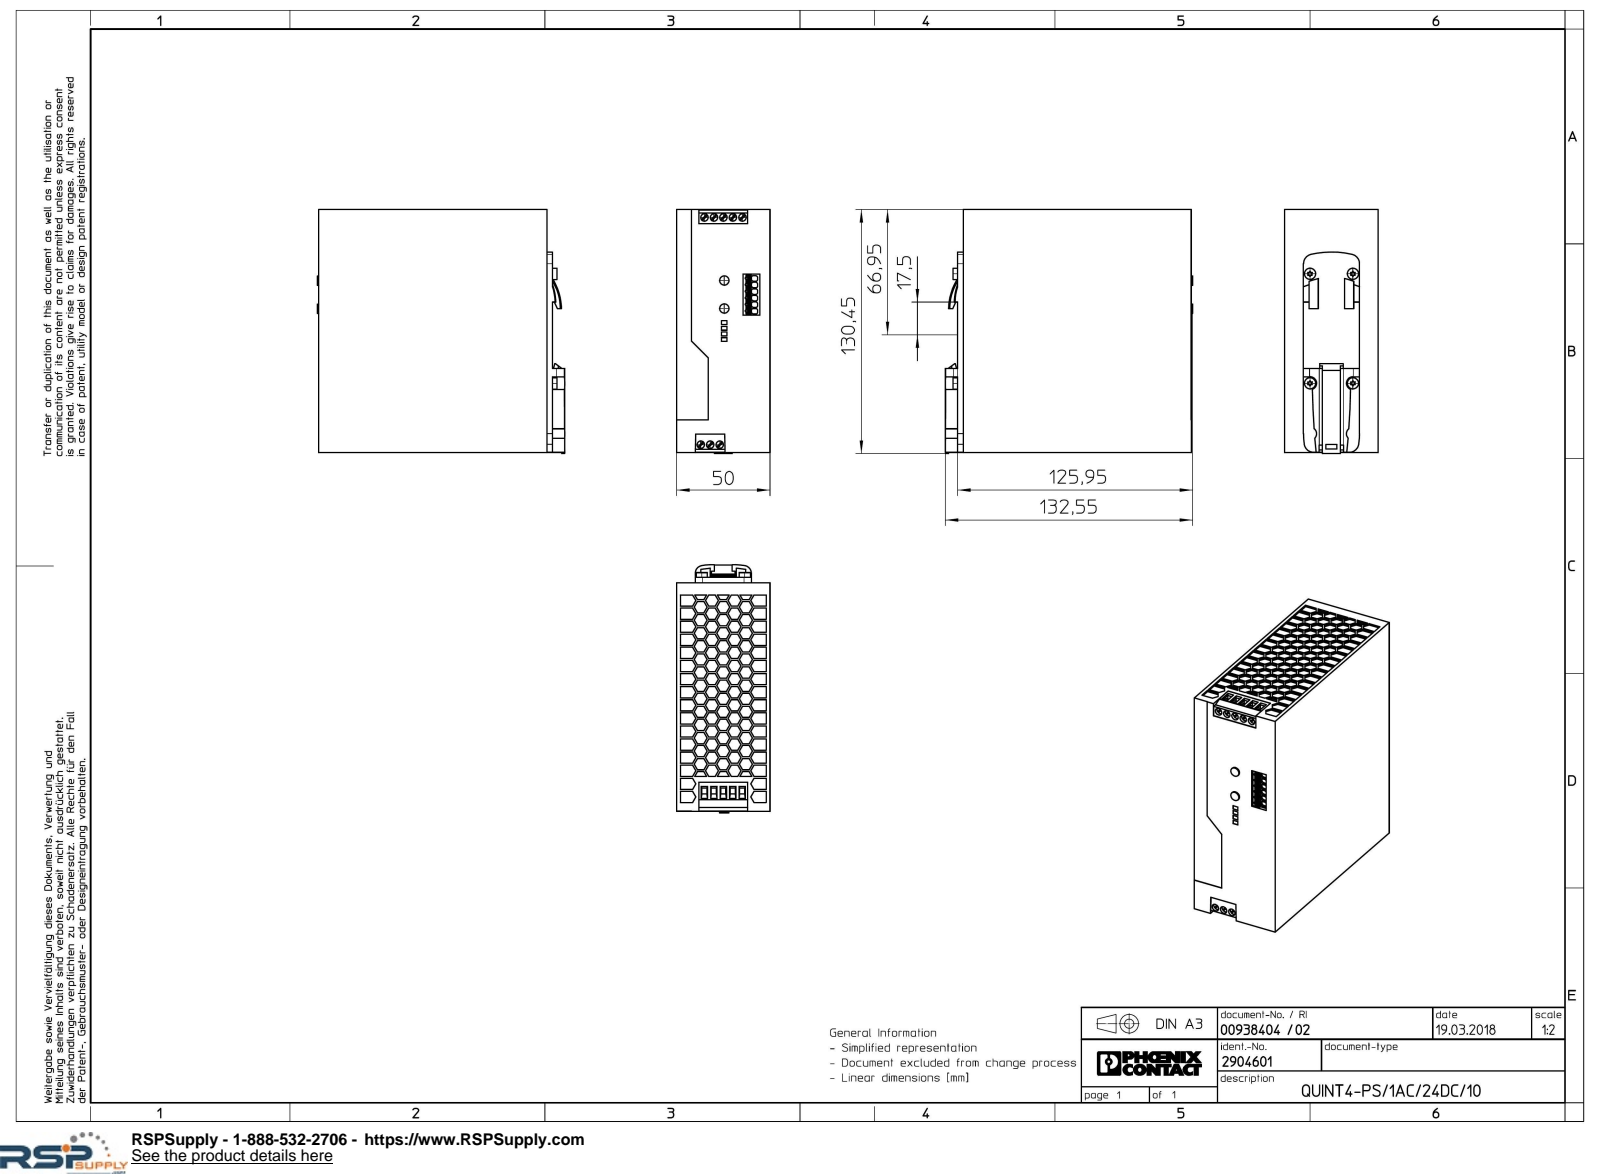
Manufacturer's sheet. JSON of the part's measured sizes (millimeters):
{"part_name": "QUINT4_PS_1AC_24DC_10-select", "step_written_by": "Creo Elements/Direct Modeling 20.1A 29-Sep-2018 (C) Parametric Technology GmbH (AUTOMOTIVE_DESIGN)", "units": "millimeters", "bodies": {"solids": 1, "faces": 1931, "planar": 1796, "cylindrical": 119, "other": 16}, "overall_size": [132.55, 130.45, 50.06], "volume_mm3": 804095, "surface_area_mm2": 64169, "round_holes": [[4, 8]], "round_bosses_or_shafts": [[6, 4], [5, 2]], "partial_cylinders_radius": [[0.1, 48], [0.97, 12], [0.57, 6], [0.6, 6], [3.5, 4], [5, 4], [4, 2], [30, 2]], "face_to_face_distances": [50.06, 0.8, 129.2, 128.4, 122.25, 130, 3, 125.25, 125.1, 122.1], "hole_center_spacings": [5.08, 10.16, 121.49, 121.67, 122.08, 15.24, 121.51, 122.68]}
